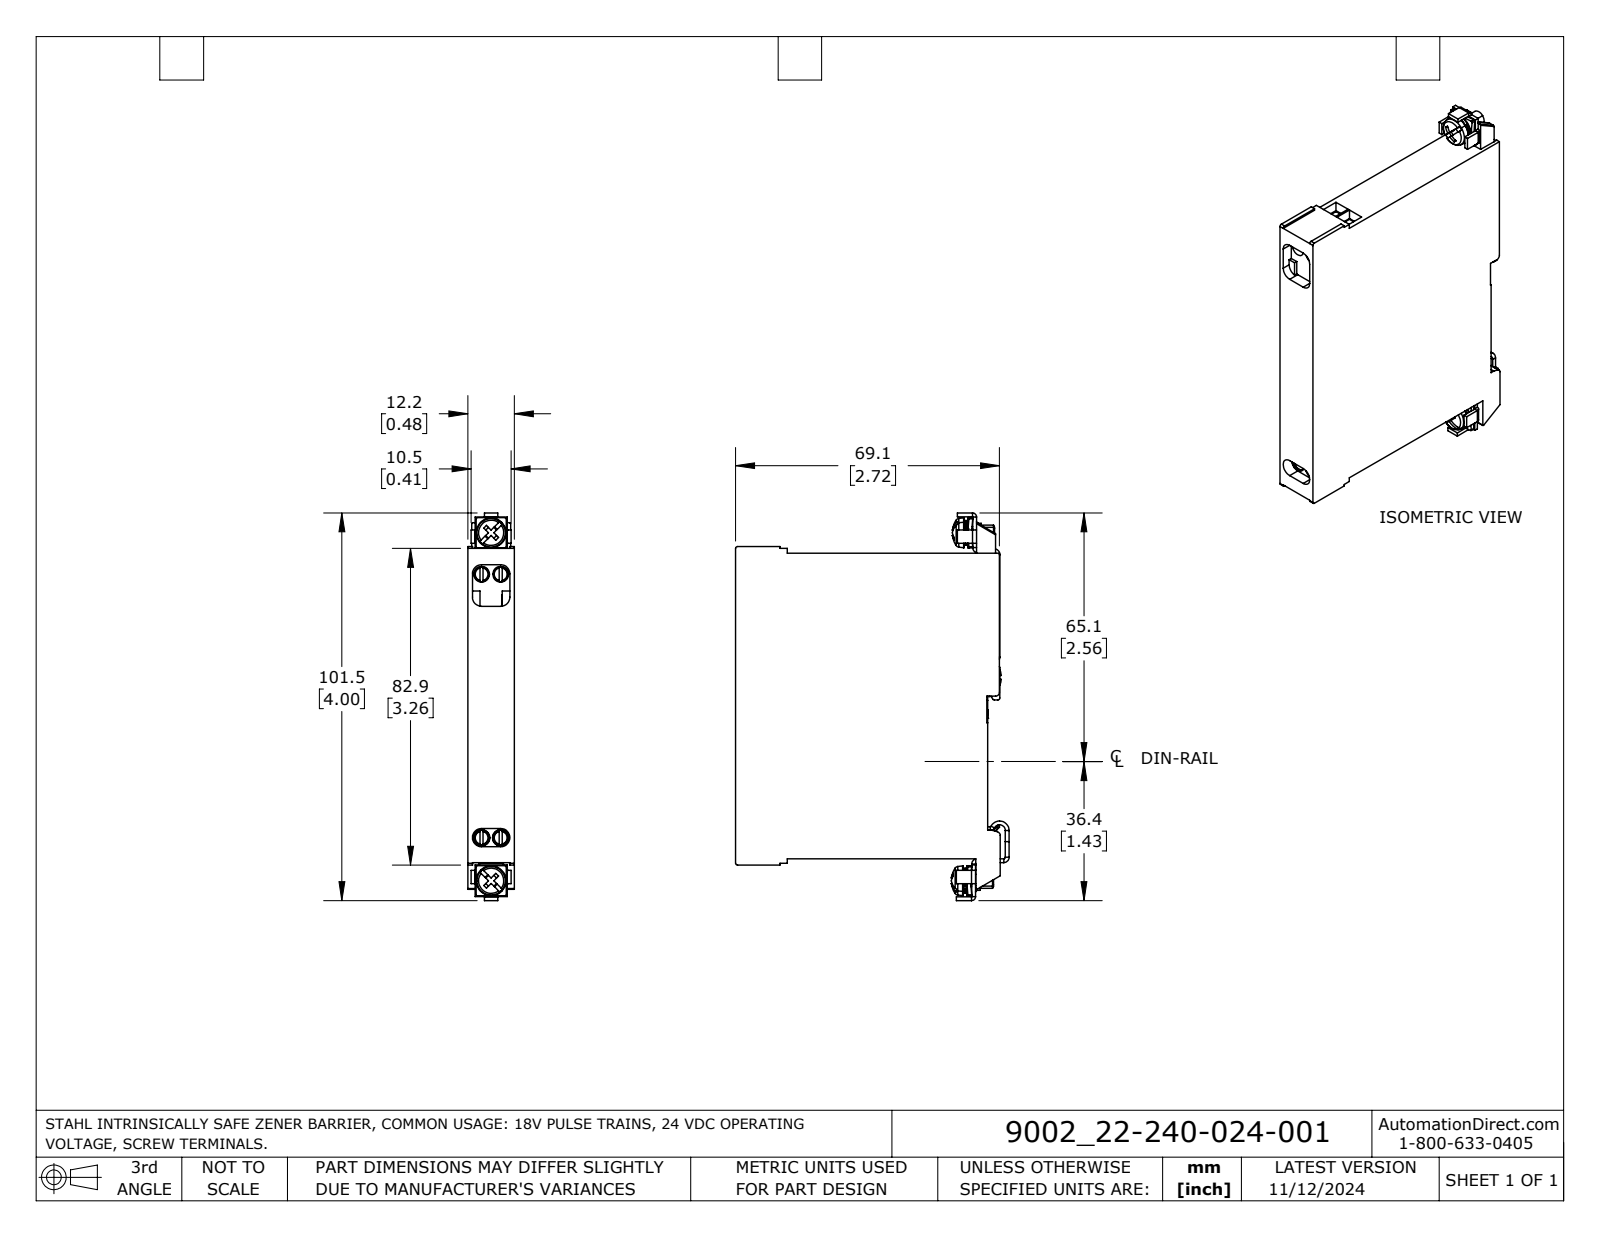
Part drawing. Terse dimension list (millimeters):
name: 900222-240-024-001
written by: SolidWorks 2023 (AUTOMOTIVE_DESIGN)
unit: mm
bodies: 4 solids, 762 faces (528 planar, 146 cylindrical, 88 other)
size: 101.5 × 71.6 × 12.2
volume: 65 250 mm³; area: 21 750 mm²
holes: 4× ⌀4.1, 3× ⌀4.3, 2× ⌀3.3, 2× ⌀4.2, 1× ⌀3
bosses: 3× ⌀7.8, 3× ⌀4, 2× ⌀5, 2× ⌀3.1, 1× ⌀6.5
rounds: 16× R0.5, 8× R0.3, 6× R0.4, 6× R1, 6× R1, 6× R1.4, 6× R2.4, 4× R0.3
face distances: 12.2, 1, 79, 1.1, 2, 78, 2.2, 80, 2.1, 1.2
hole spacings: 5, 11.1, 11.5, 27.1, 28.2, 41, 42.1, 69
